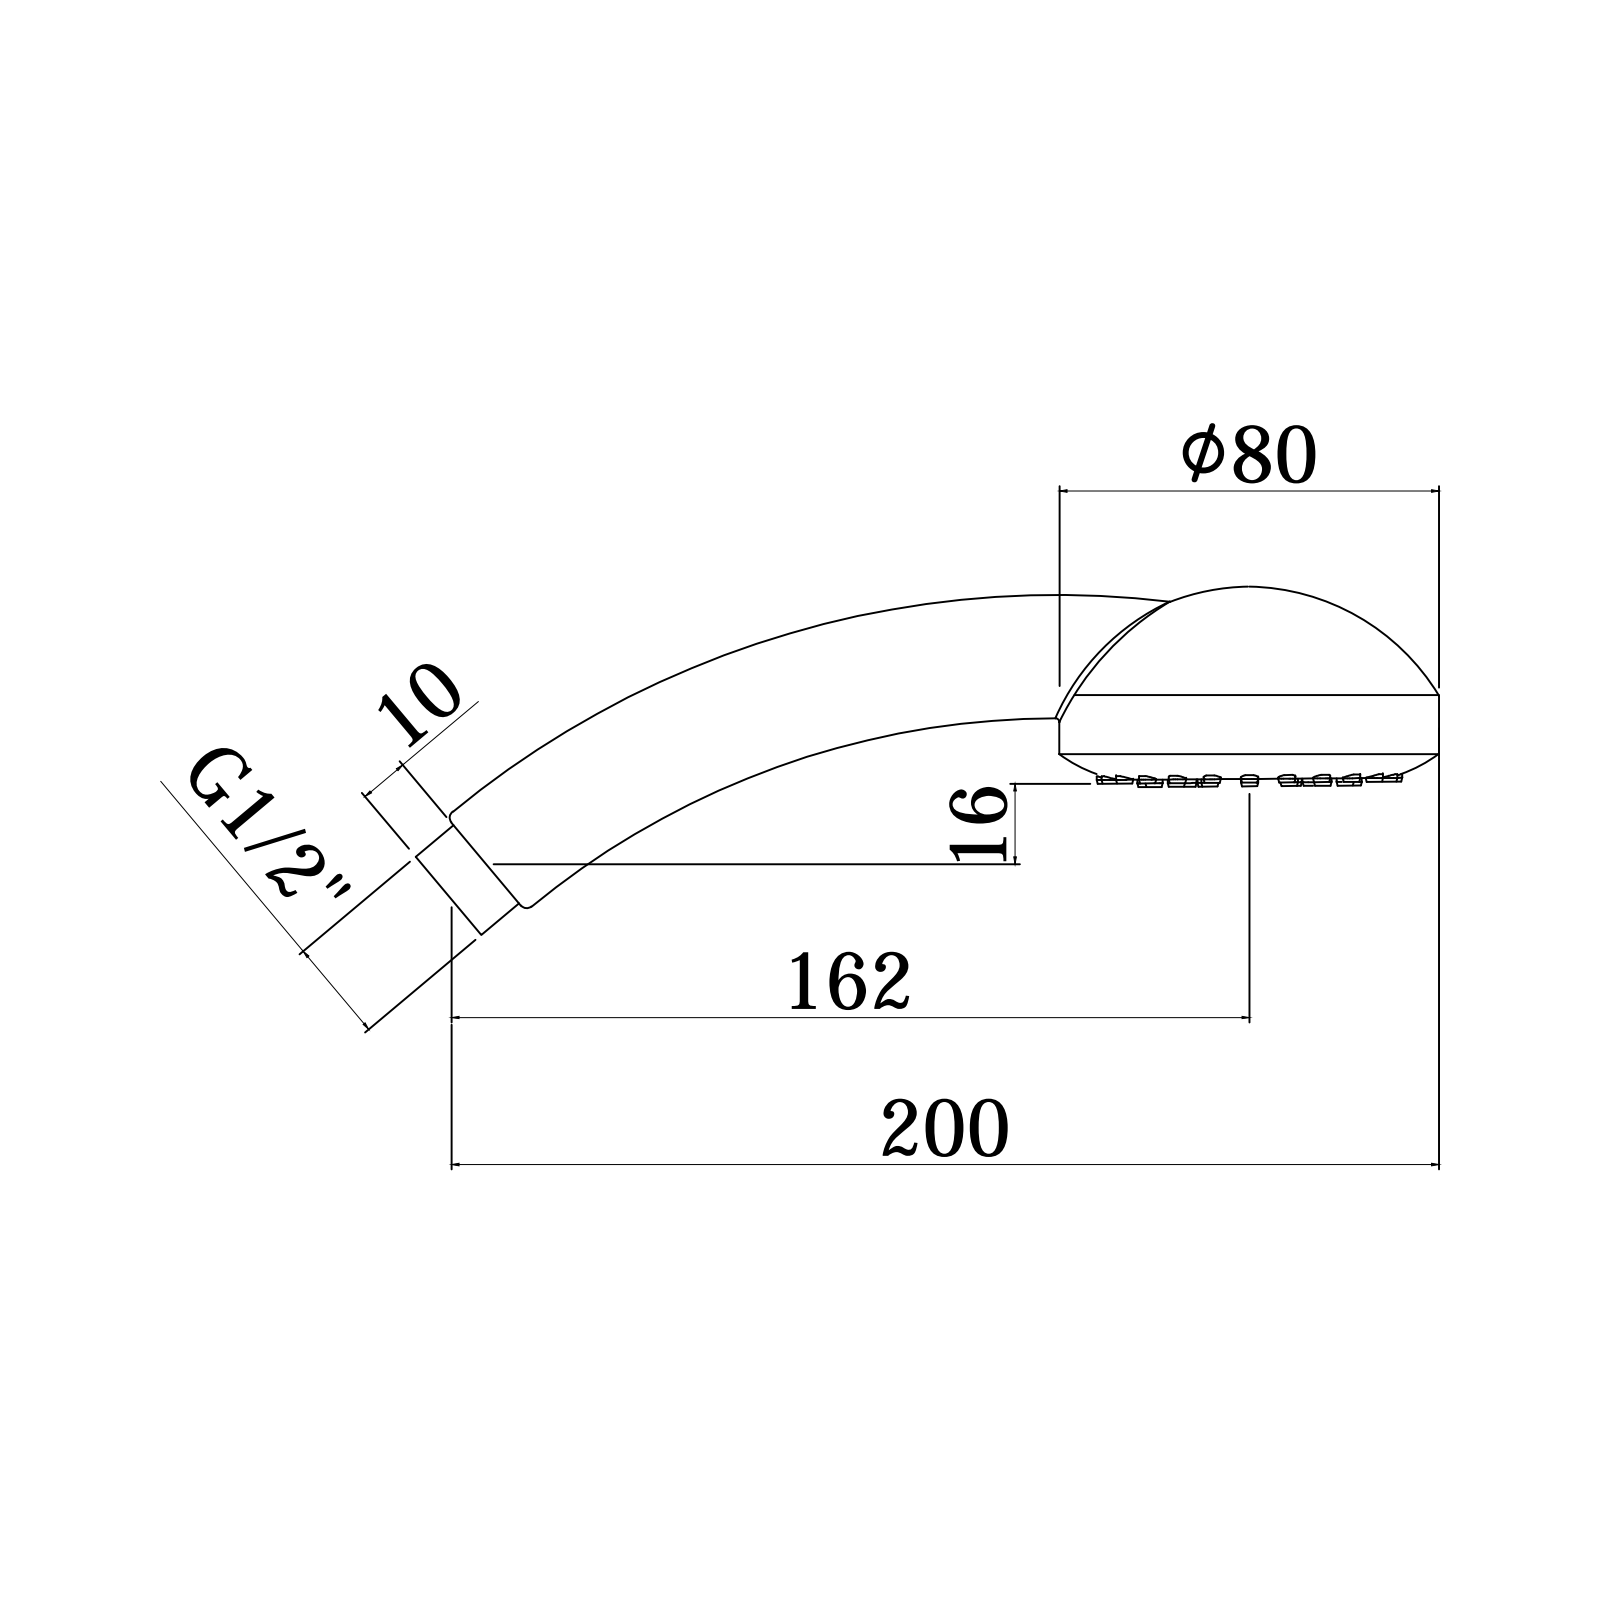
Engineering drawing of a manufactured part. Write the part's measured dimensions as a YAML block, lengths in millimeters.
part_name: "ZDOC081CR"
step_written_by: "CREO PARAMETRIC BY PTC INC, 2020044 (CONFIG_CONTROL_DESIGN)"
units: millimeters
bodies: {solids: 2, faces: 664, planar: 149, cylindrical: 92, other: 423}
overall_size: [218.63, 80.95, 80.3]
volume: 138611
surface_area: 56893
round_holes:
  - {diameter: 3.25, count: 1}
  - {diameter: 3.31, count: 1}
  - {diameter: 4.5, count: 1}
  - {diameter: 9.63, count: 1}
  - {diameter: 12.83, count: 1}
  - {diameter: 13.2, count: 1}
  - {diameter: 14, count: 1}
  - {diameter: 15, count: 1}
  - {diameter: 19, count: 1}
  - {diameter: 69.4, count: 1}
  - {diameter: 76, count: 1}
round_bosses_or_shafts:
  - {diameter: 75.5, count: 1}
  - {diameter: 72.5, count: 1}
  - {diameter: 65.8, count: 1}
  - {diameter: 20.6, count: 1}
  - {diameter: 17.2, count: 1}
  - {diameter: 15.03, count: 1}
  - {diameter: 14.6, count: 1}
  - {diameter: 9.31, count: 1}
partial_cylinders:
  - {radius: 0.75, count: 16}
  - {radius: 0.5, count: 12}
  - {radius: 3.65, count: 2}
  - {radius: 3.8, count: 2}
  - {radius: 5, count: 2}
  - {radius: 15.89, count: 2}
  - {radius: 16.04, count: 2}
  - {radius: 16.27, count: 2}
face_to_face_distances: [7, 2.07, 2.74, 0.67, 9.74, 7.67, 2, 5.2, 3.13, 2.46]
hole_center_spacings: [10.5, 10.51, 14.35, 24.85, 24.86]
